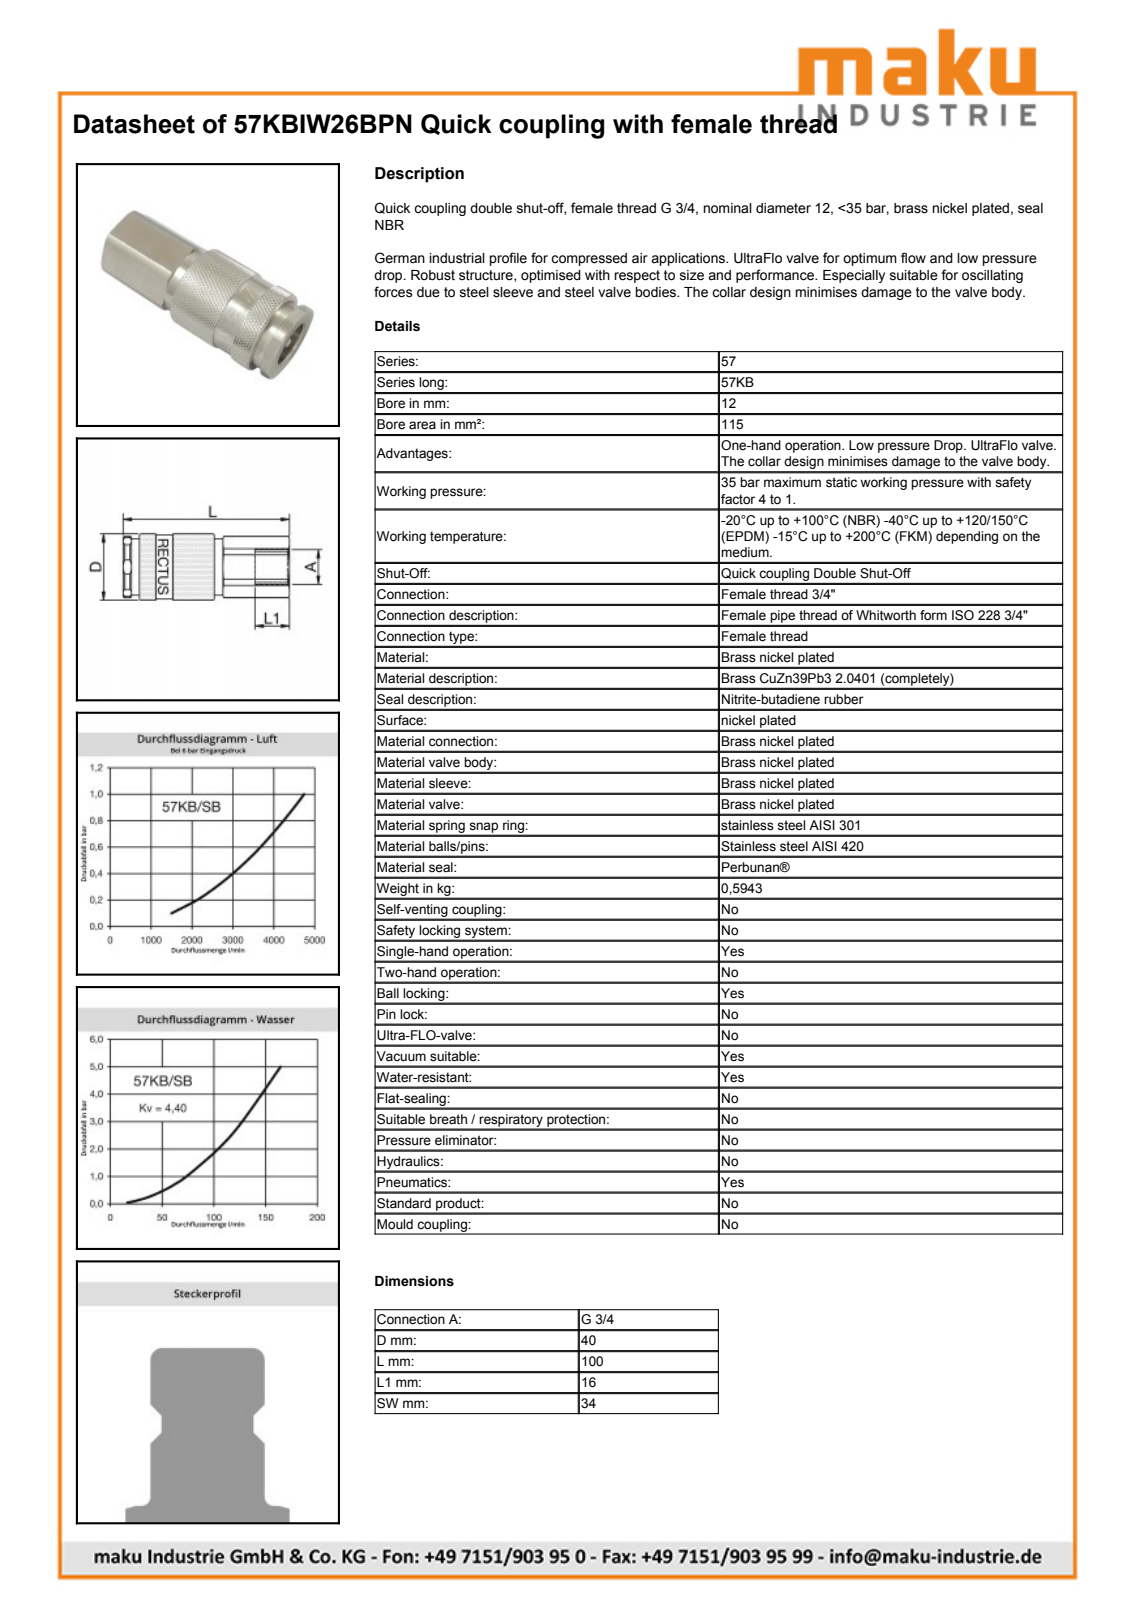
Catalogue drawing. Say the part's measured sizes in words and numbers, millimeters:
The part is named "D111143". Its 3-D file was written by "Autodesk Inventor 2013 (AUTOMOTIVE_DESIGN)". It is 2 solids with 506 faces: 200 planar, 72 cylindrical and 234 other. Overall it measures 100.05 by 40 by 40 millimeters. Its volume is 94 356 cubic millimeters and its surface area 27 349 square millimeters. Round holes: 1 of diameter 24.12, 1 of diameter 28.95, 1 of diameter 30, 1 of diameter 30.2, 1 of diameter 34.2, 1 of diameter 34.6. Round bosses or shafts: 1 of diameter 40, 1 of diameter 38.5, 1 of diameter 34, 1 of diameter 28.8, 1 of diameter 28.4, 1 of diameter 27.25. Partial cylindrical surfaces (rounded edges, fillets, slot ends): 1 of radius 18.5, 1 of radius 19.15. The main face-to-face distances are 34, 77.07, 100.05, 22.98, 37.8, 39.27, 62.25, 8.8, 29, 68.27.
